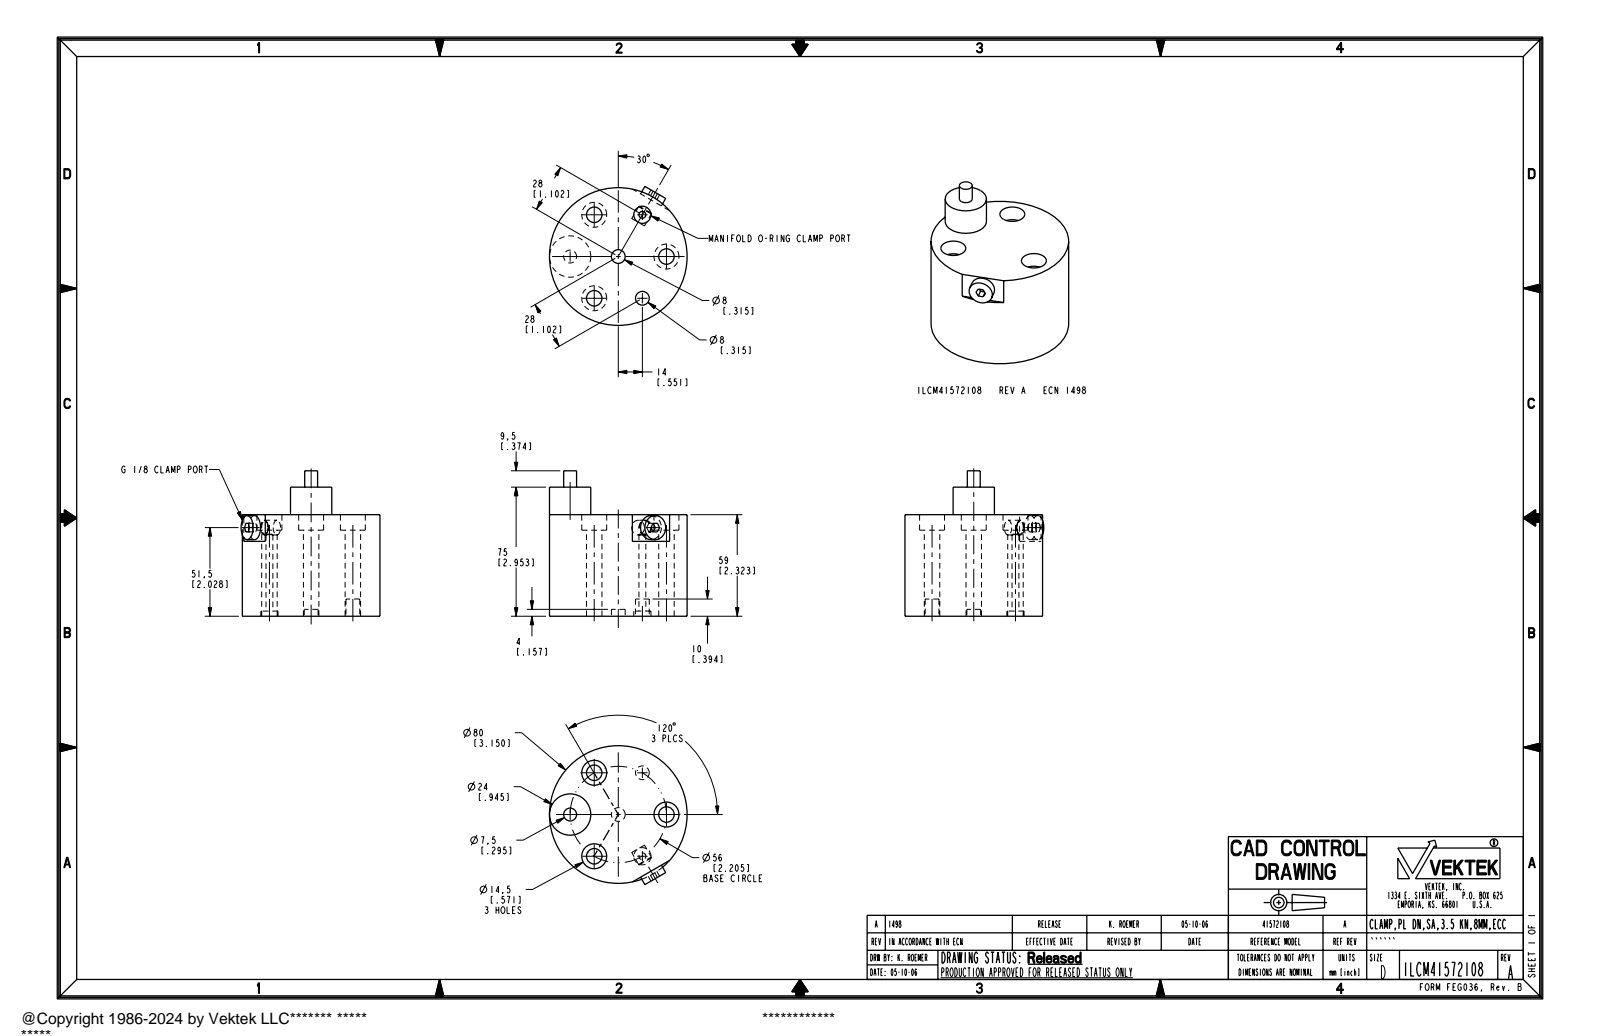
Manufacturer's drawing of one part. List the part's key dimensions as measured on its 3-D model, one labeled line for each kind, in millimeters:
Part name (STEP PRODUCT): ILCM41572108
STEP written by: PRO/ENGINEER BY PARAMETRIC TECHNOLOGY CORPORATION, 2004290 (AUTOMOTIVE_DESIGN_CC2)
Units: millimetres
Bodies: 1 solid, 54 faces (22 planar, 30 cylindrical, 2 other)
Overall size (bounding box): 84.5 × 80.74 × 80
Volume: 288 406 mm³ · Surface area: 33 027 mm²
Round holes (diameter × count): ⌀9 ×3, ⌀14.5 ×3, ⌀8 ×2, ⌀4 ×1, ⌀8.57 ×1, ⌀10 ×1
Round bosses / shafts (diameter × count): ⌀80 ×1, ⌀24 ×1, ⌀14 ×1, ⌀7.5 ×1
Main face-to-face distances: 59, 75, 16, 50, 9, 25, 5, 7, 3, 47
Hole centre spacings: 28, 48.5, 56
